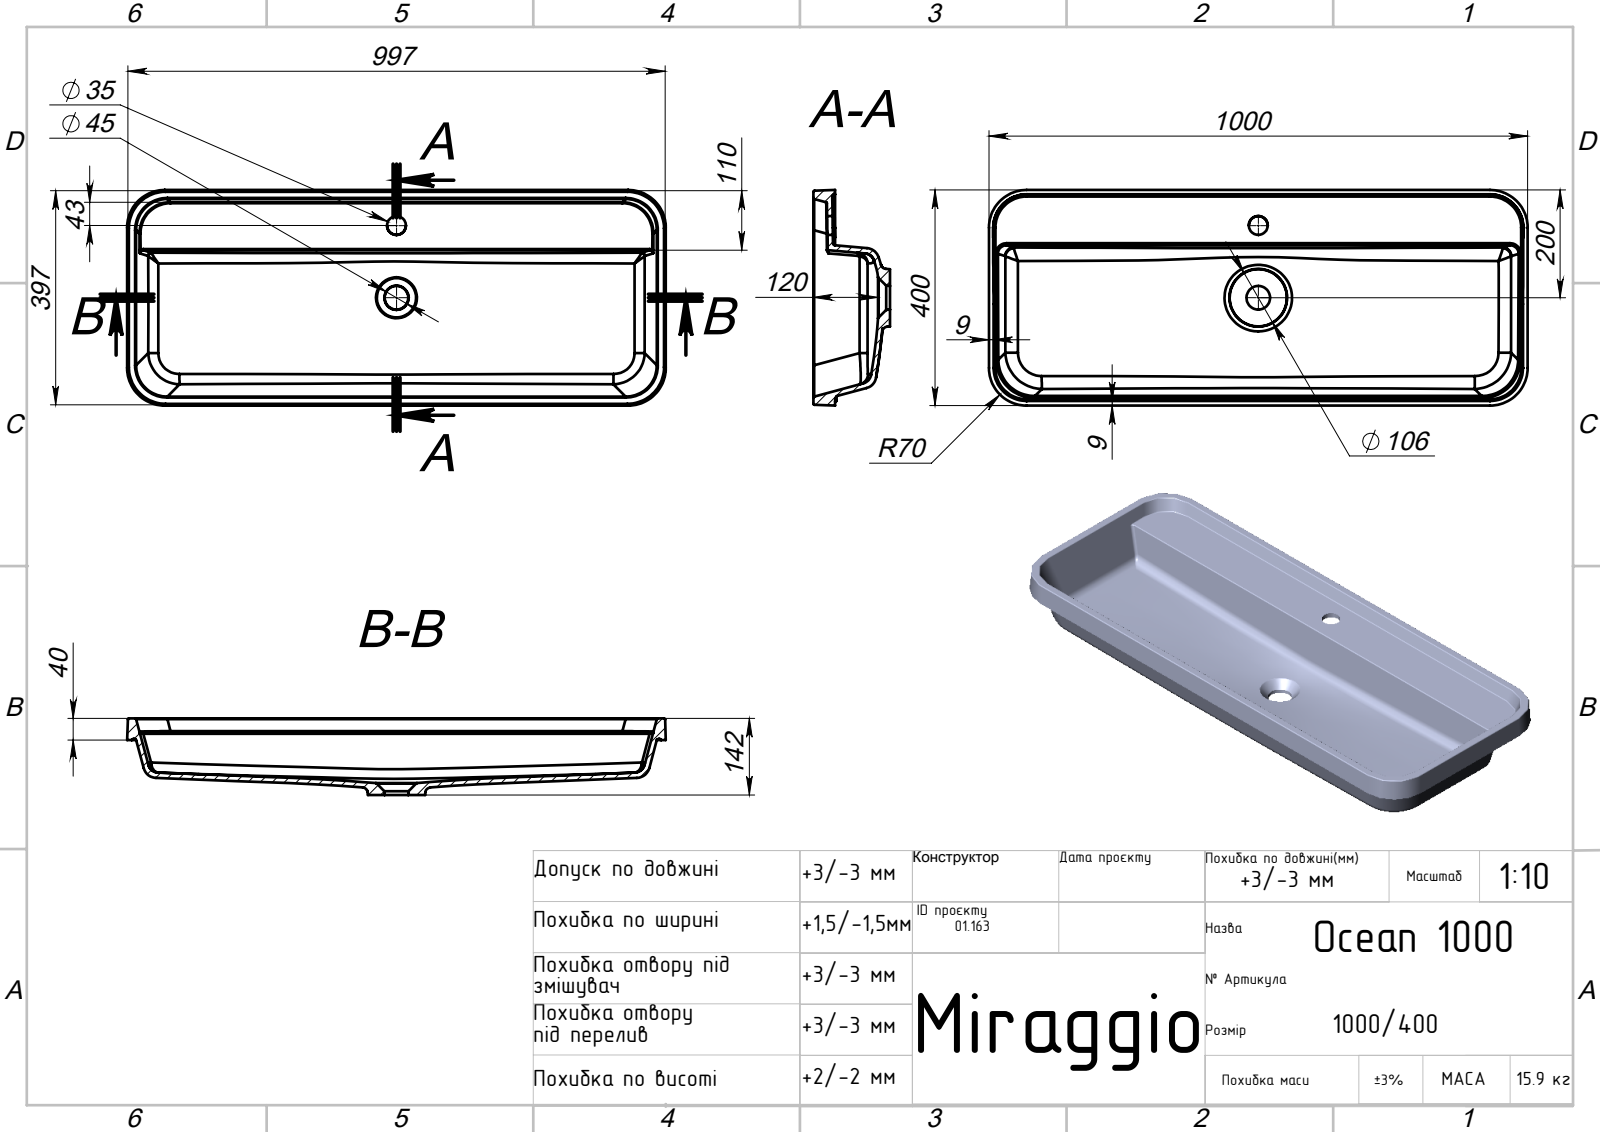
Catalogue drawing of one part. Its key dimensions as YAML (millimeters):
part_name: "Ocean 1000"
step_written_by: "SolidWorks 2020 (AUTOMOTIVE_DESIGN)"
units: millimeters
bodies: {solids: 1, faces: 121, planar: 22, cylindrical: 42, other: 57}
overall_size: [1000, 400, 142]
volume: 6615000
surface_area: 1221000
round_holes:
  - {diameter: 35, count: 1}
partial_cylinders:
  - {radius: 5, count: 16}
  - {radius: 70, count: 6}
  - {radius: 2, count: 4}
  - {radius: 60, count: 4}
  - {radius: 62, count: 4}
  - {radius: 1, count: 3}
  - {radius: 6, count: 2}
  - {radius: 16, count: 2}
face_to_face_distances: [10, 9.99, 5, 15, 40, 35, 25, 102, 107, 117]
